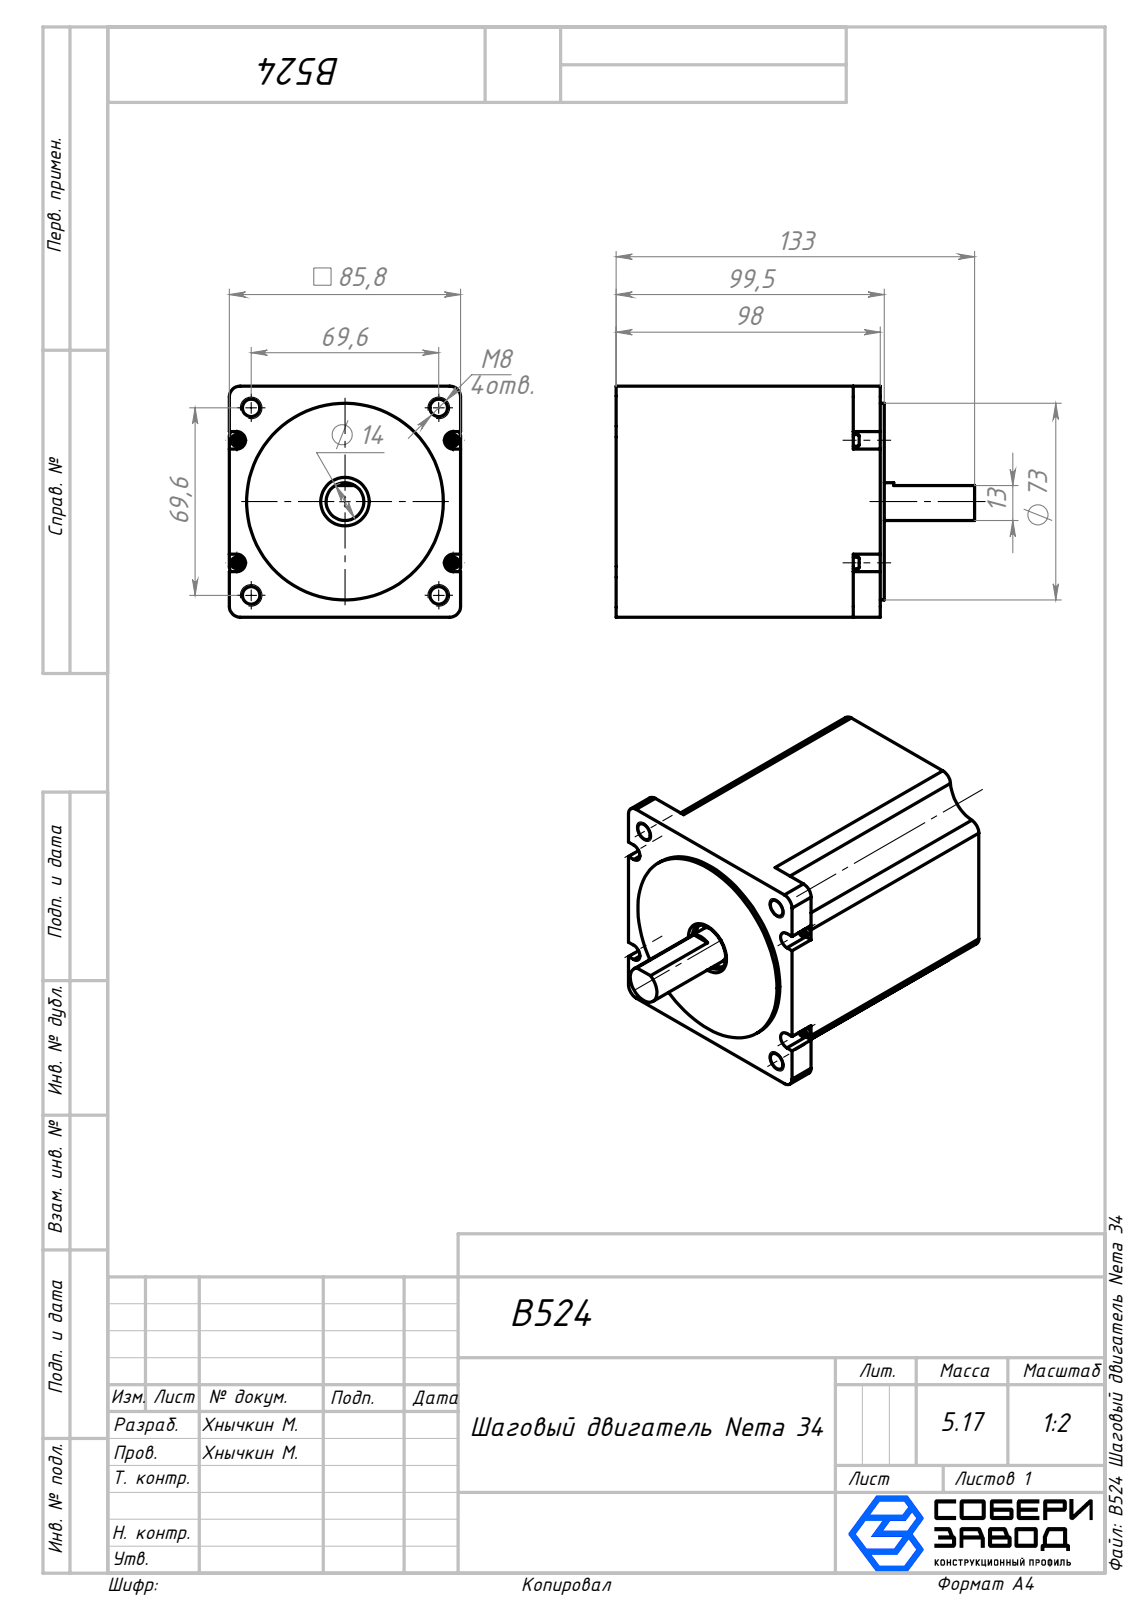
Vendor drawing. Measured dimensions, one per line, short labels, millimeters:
name: B524 Шаговый двигатель Nema 34
written by: SolidWorks 2026 (AUTOMOTIVE_DESIGN)
unit: mm
bodies: 1 solid, 150 faces (90 planar, 50 cylindrical, 10 other)
size: 133 × 85.8 × 85.8
volume: 659 139 mm³; area: 48 882 mm²
holes: 4× ⌀6.5, 1× ⌀10, 1× ⌀16, 1× ⌀18
bosses: 4× ⌀4.3, 1× ⌀73, 1× ⌀14, 1× ⌀6.35
rounds: 12× R4, 4× R3.25, 4× R12
face distances: 85.8, 99.5, 1.5, 98, 88, 10, 11.5, 48.9, 36.9, 4
hole spacings: 49.21, 69.6, 98.43
